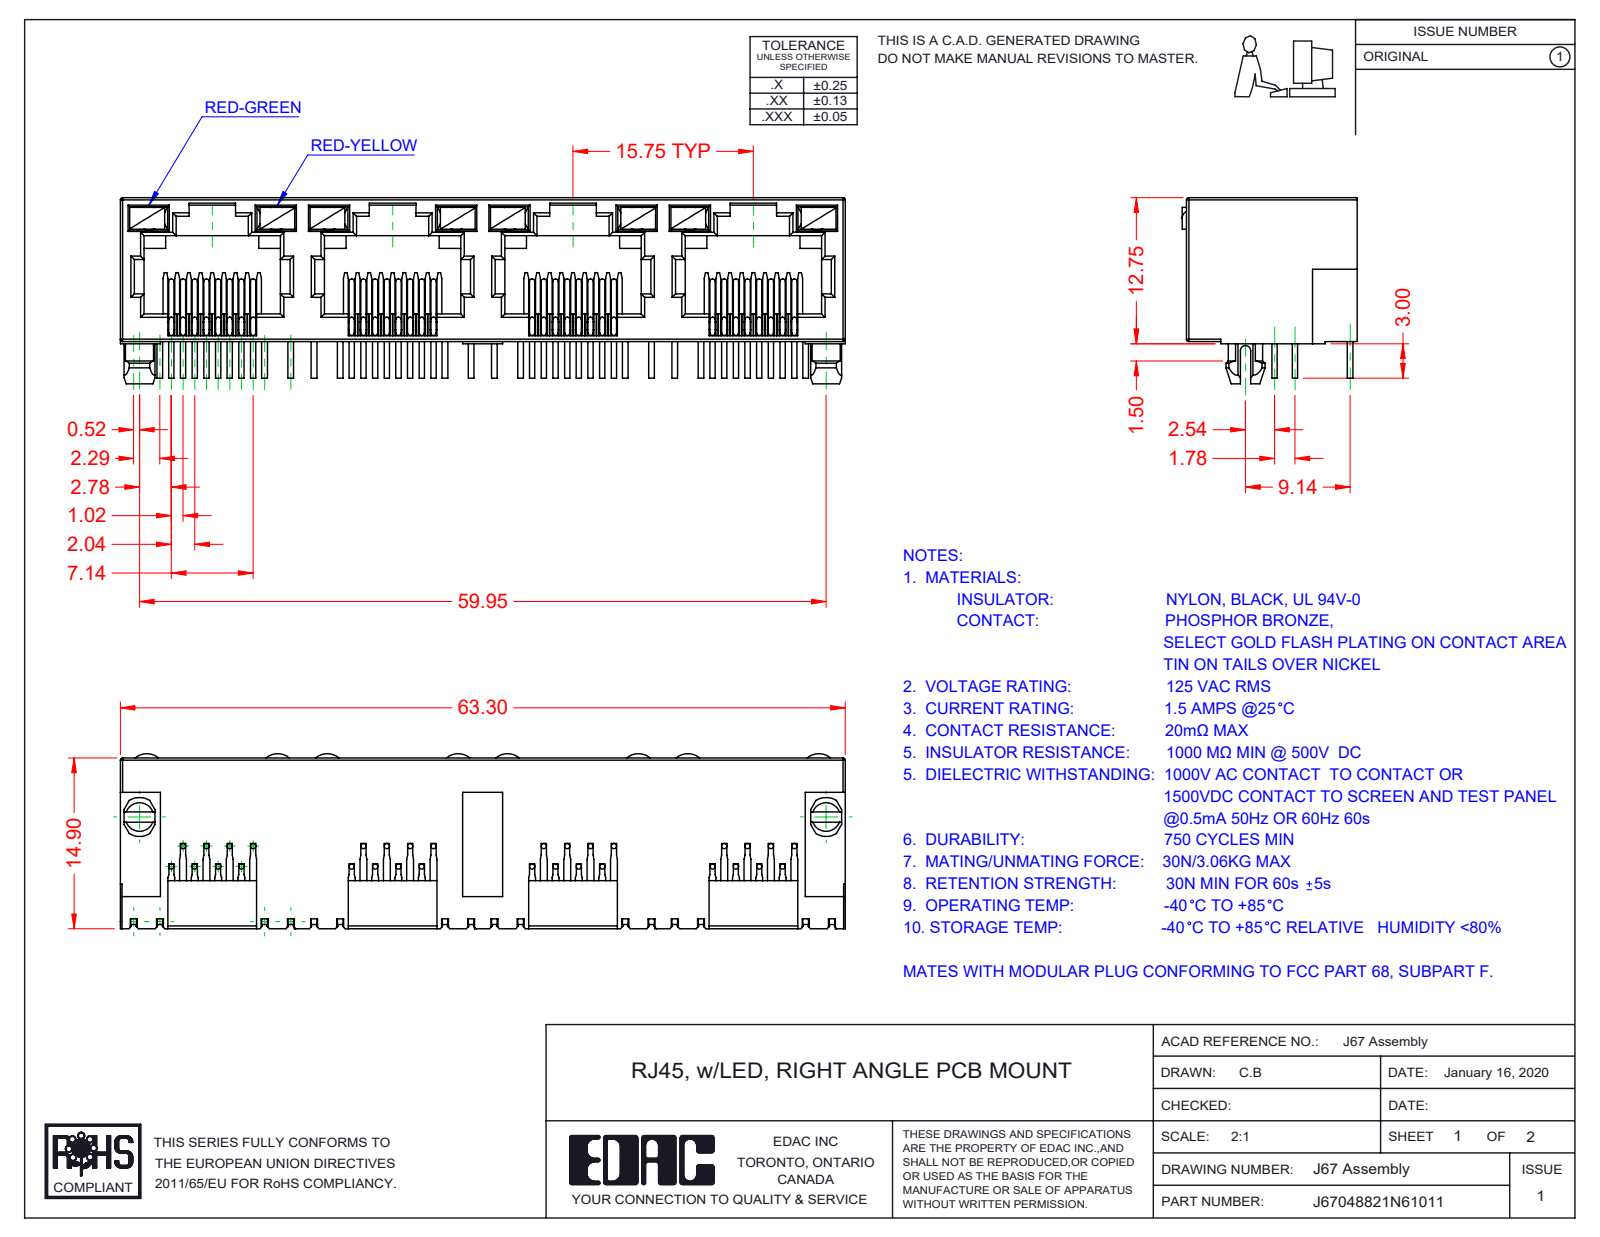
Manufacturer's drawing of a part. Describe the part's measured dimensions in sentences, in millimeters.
The part is named "67 LED RH_8-Red-Yellow; J67048822N68011; 67 Contacts; 67 Insulator (+1 more)". Its 3-D file was written by "SolidWorks 2016 (CONFIG_CONTROL_DESIGN)". It is 41 solids with 2481 faces: 1781 planar, 492 cylindrical and 208 other. Overall it measures 63.3 by 16.25 by 15.28 millimeters. Its volume is 5 159 cubic millimeters and its surface area 11 573 square millimeters. Round bosses or shafts: 96 of diameter 0.46. Partial cylindrical surfaces (rounded edges, fillets, slot ends): 66 of radius 0.2, 29 of radius 0.3, 9 of radius 0.45, 8 of radius 1.55, 2 of radius 1.5, 2 of radius 1.7, 1 of radius 0.35, 1 of radius 1. The main face-to-face distances are 0.5, 12.55, 1.89, 0.89, 10, 15.75, 1, 1.39, 11, 11.89.
